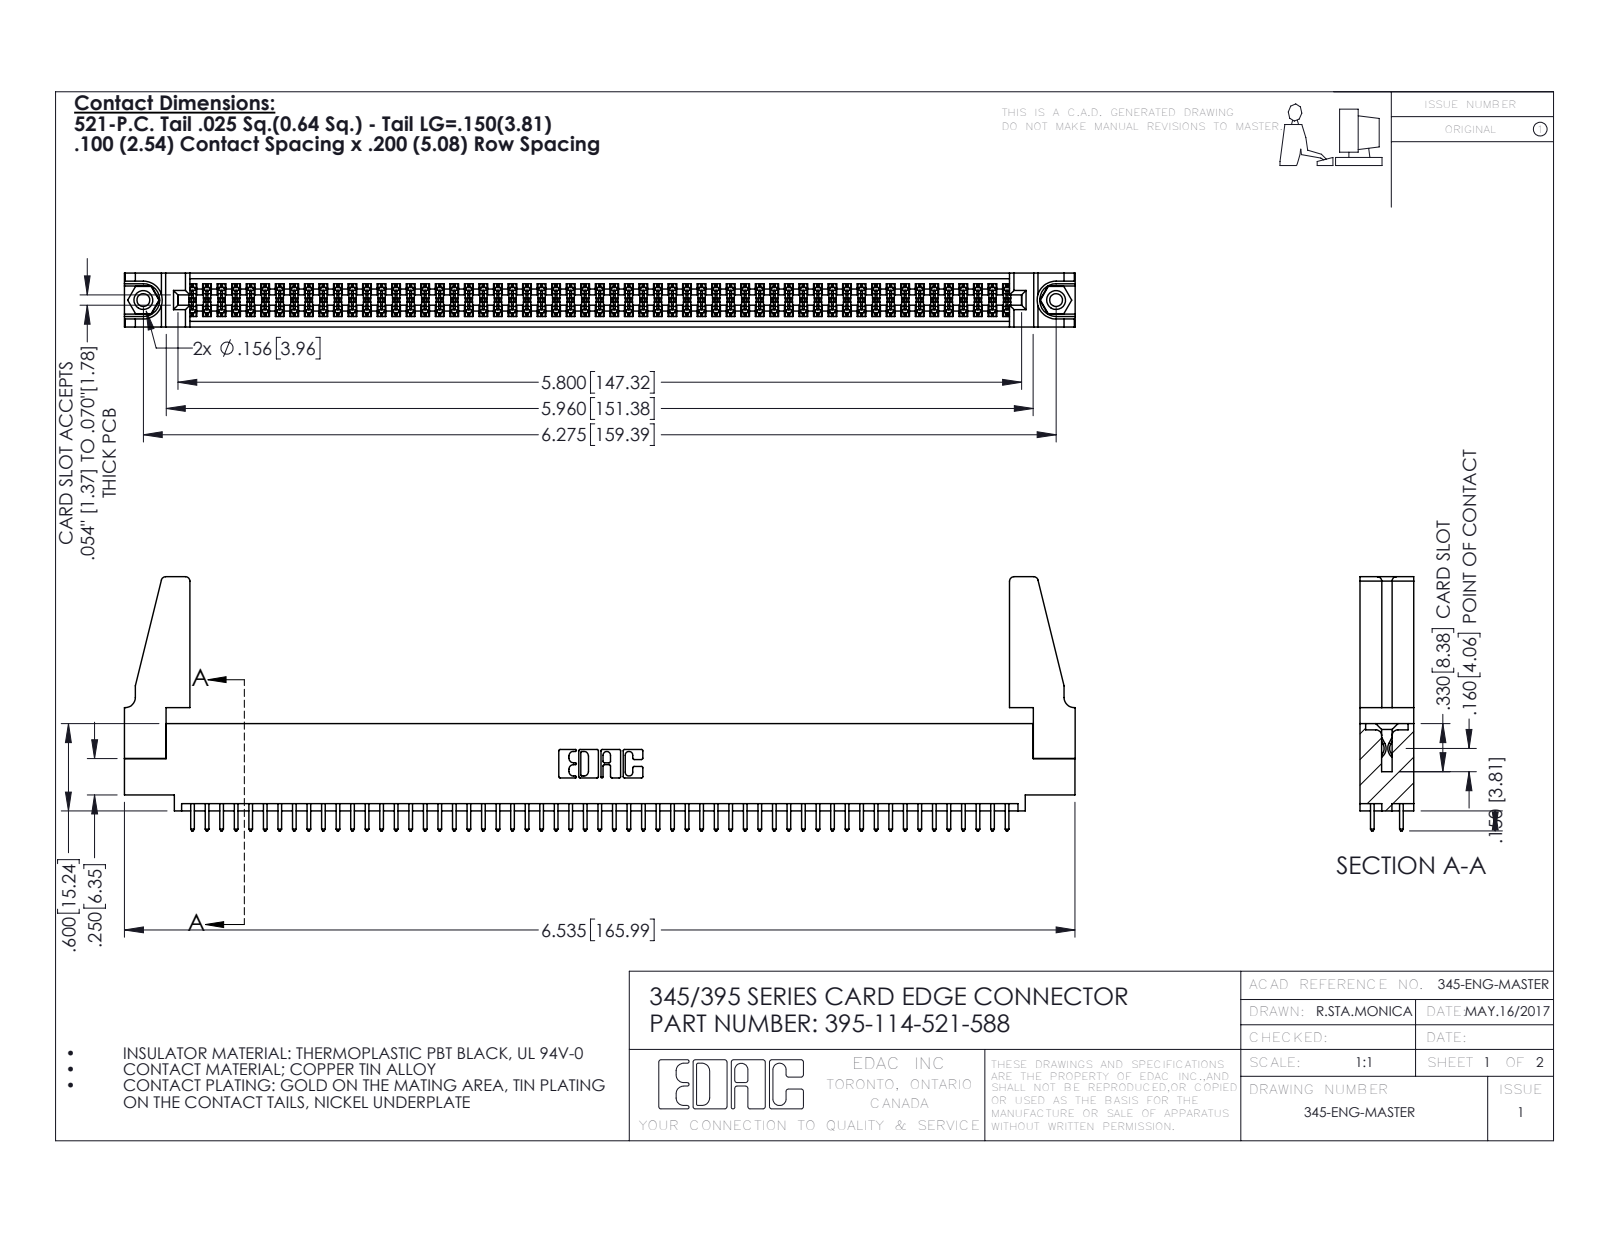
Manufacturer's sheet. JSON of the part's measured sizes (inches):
{"part_name": "345 Part_0.110 Offset - 0.156 Dia-TH; 345-250-001_345-250-001-102; 345-292-001_345-293-121; 345-220-078_345-220-088 (+1 more)", "step_written_by": "SolidWorks 2016 (CONFIG_CONTROL_DESIGN)", "units": "inches", "bodies": {"solids": 119, "faces": 5954, "planar": 3918, "cylindrical": 2020, "other": 16}, "overall_size": [6.536, 1.747, 0.37], "volume_in3": 1.184, "surface_area_in2": 41.96, "round_holes": [[0.089, 2], [0.125, 2], [0.156, 2], [0.064, 1]], "round_bosses_or_shafts": [[0.155, 2]], "partial_cylinders_radius": [[0.006, 171], [0.01, 114], [0.01, 22], [0.03, 8], [0.007, 6], [0.031, 6], [0.026, 3], [0.014, 2]], "face_to_face_distances": [0.072, 0.298, 0.37, 0.2, 0.098, 0.272, 0.025, 0.225, 0.175, 0.149], "hole_center_spacings": [0.27, 6.039, 6.275]}
